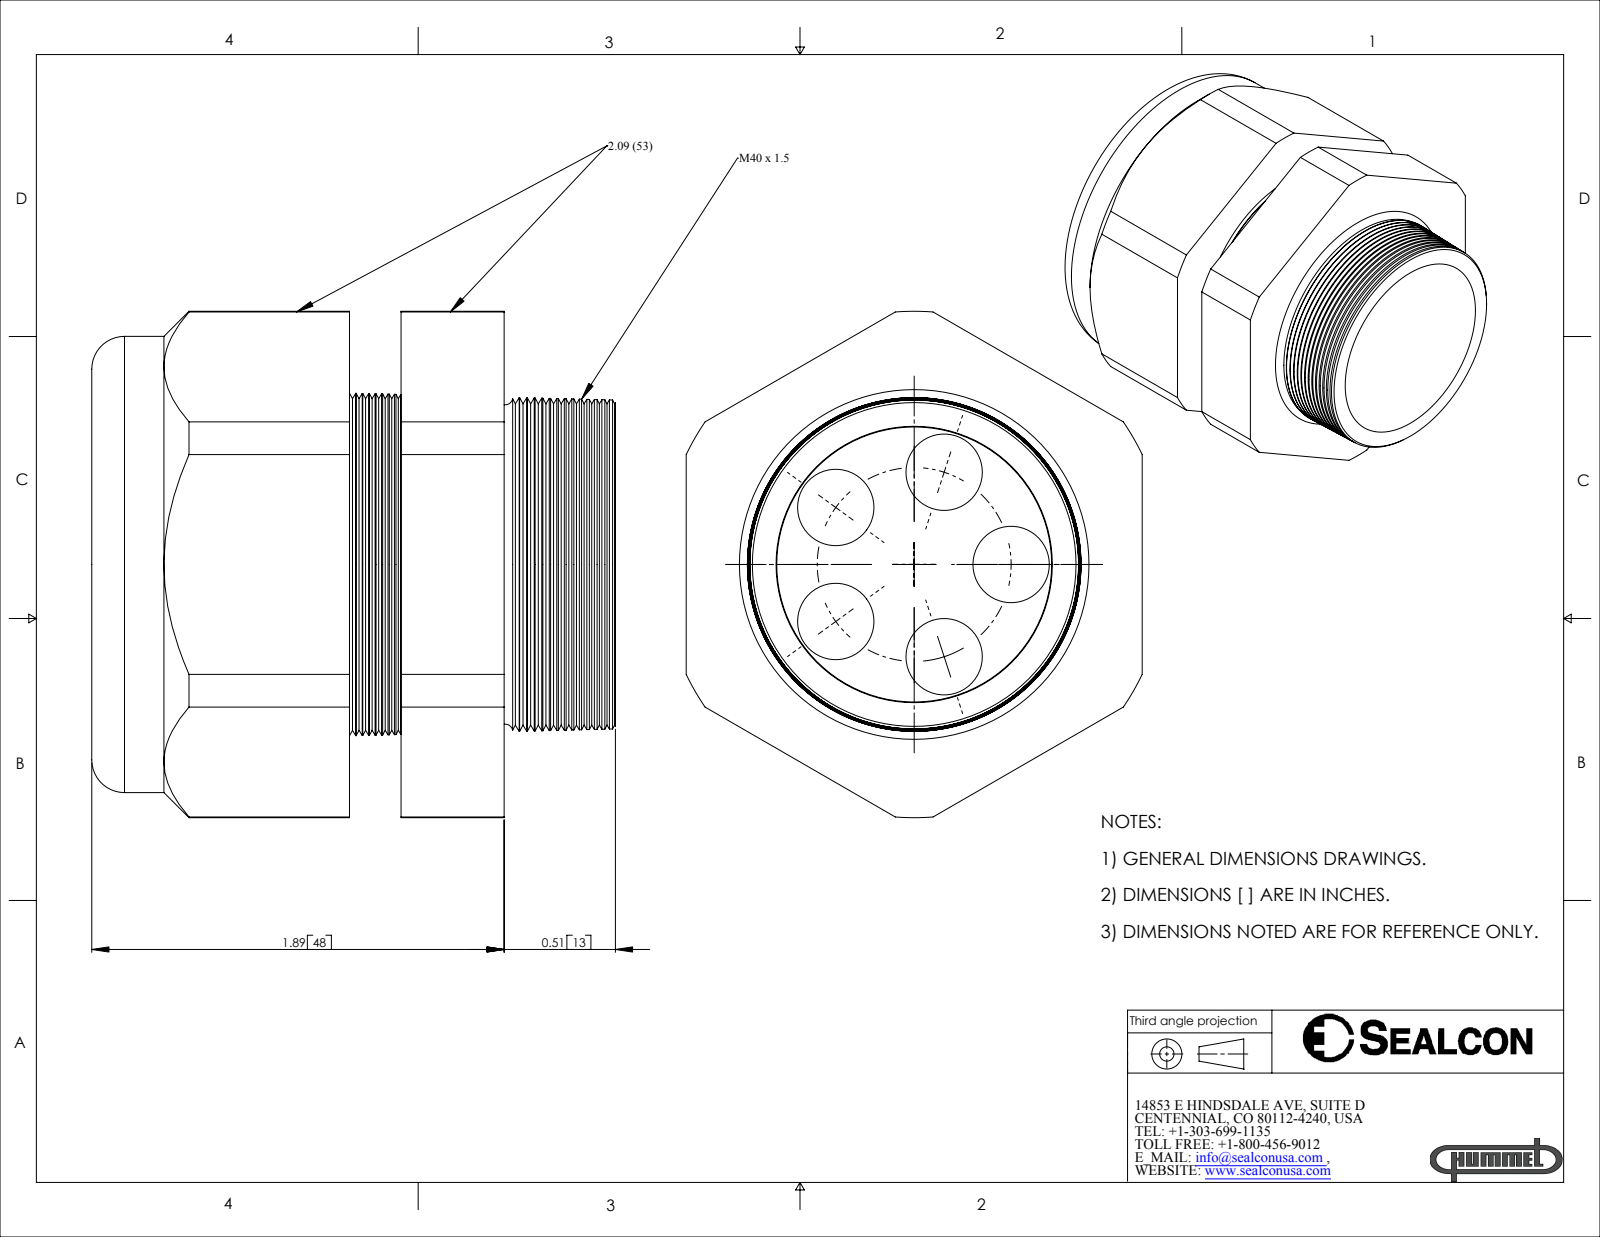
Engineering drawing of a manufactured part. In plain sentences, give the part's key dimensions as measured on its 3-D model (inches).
The part is named "CD40M1-BK". Its 3-D file was written by "SolidWorks 2007 (CONFIG_CONTROL_DESIGN)". It is 2 solids with 199 faces: 21 planar, 30 cylindrical and 148 other. Overall it measures 2.4 by 2.32 by 2.09 inches. Its volume is 4.765 cubic inches and its surface area 41.84 square inches. Round holes: 5 of diameter 0.35, 1 of diameter 1.24, 1 of diameter 1.26. Round bosses or shafts: 1 of diameter 2.09. Partial cylindrical surfaces (rounded edges, fillets, slot ends): 1 of radius 1.16. The main face-to-face distances are 2.09, 0.237, 0.709, 0.472, 1.181, 1.418, 1.89, 0.5, 0.681, 0.918. The hole center spacings are 0.444, 0.522, 0.845, 0.845, 0.444, 0.522.
